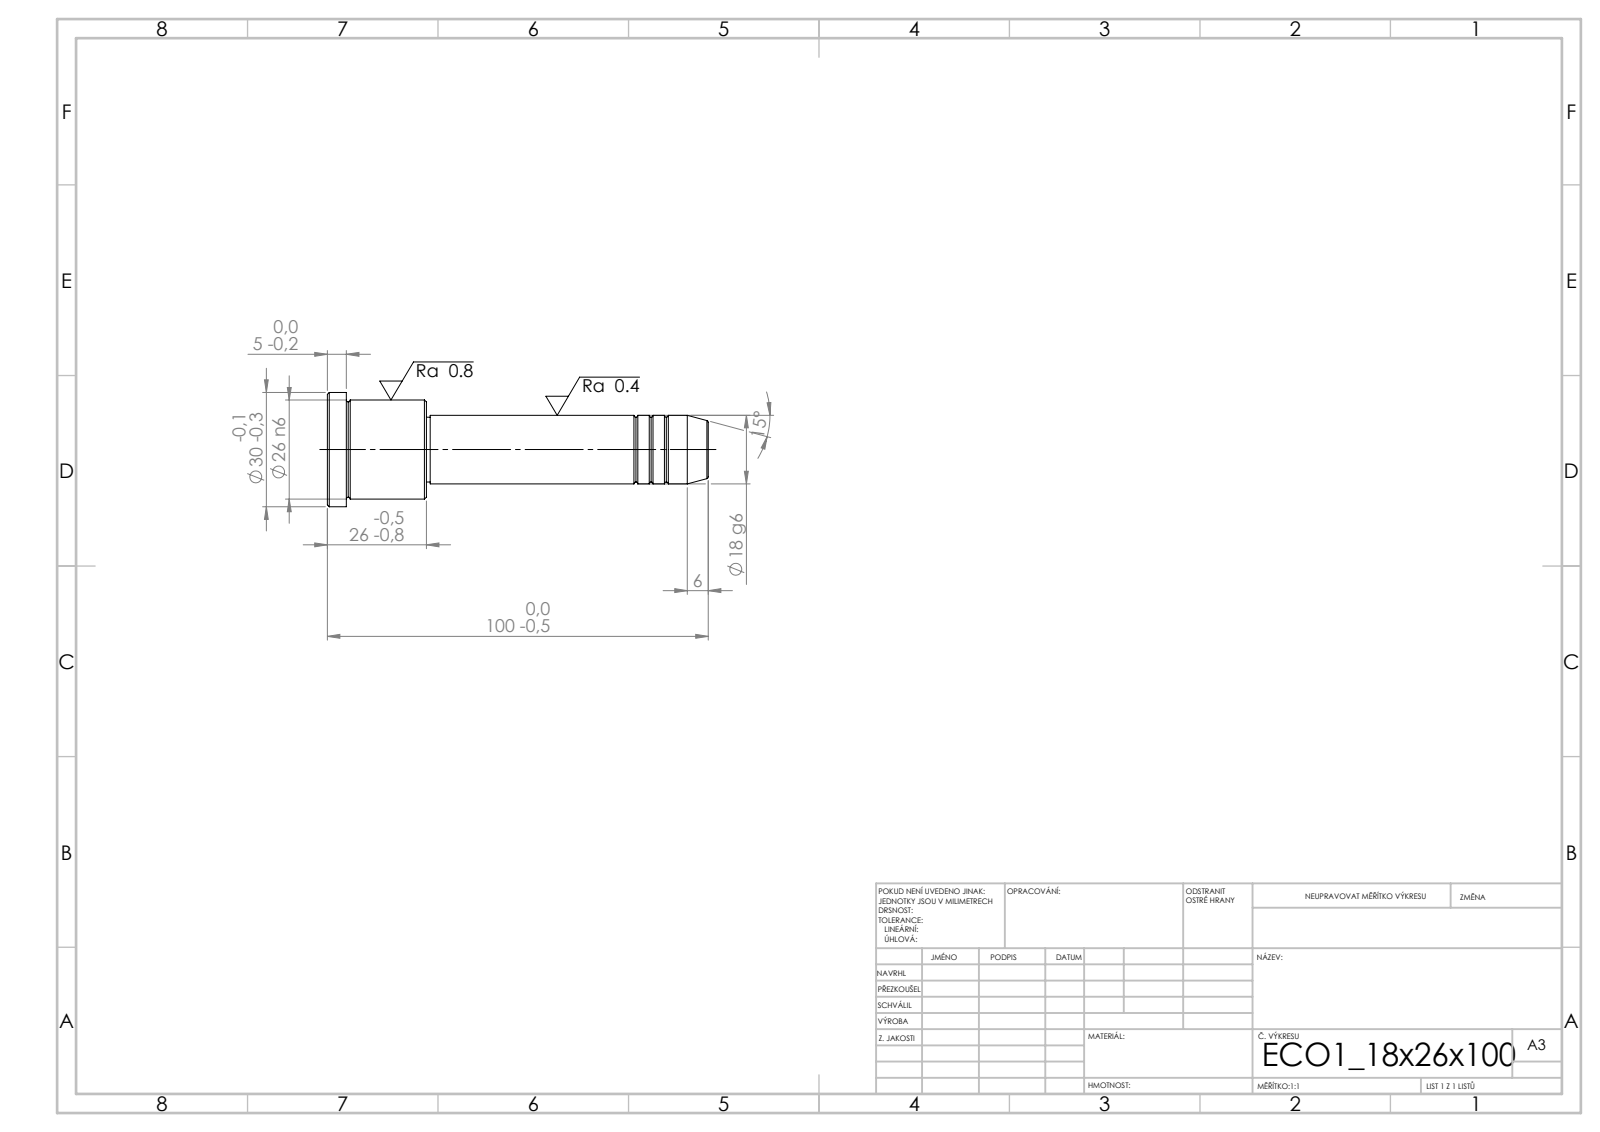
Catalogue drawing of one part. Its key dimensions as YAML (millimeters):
step_written_by: "SolidWorks 2019 (CONFIG_CONTROL_DESIGN)"
units: millimeters
bodies: {solids: 1, faces: 43, planar: 5, cylindrical: 14, other: 24}
overall_size: [100, 30, 30]
volume: 33151
surface_area: 7818
round_bosses_or_shafts:
  - {diameter: 30, count: 1}
  - {diameter: 26, count: 1}
  - {diameter: 18, count: 1}
  - {diameter: 17, count: 1}
face_to_face_distances: [26, 21, 5, 74, 95, 100, 73, 1, 22, 27]
